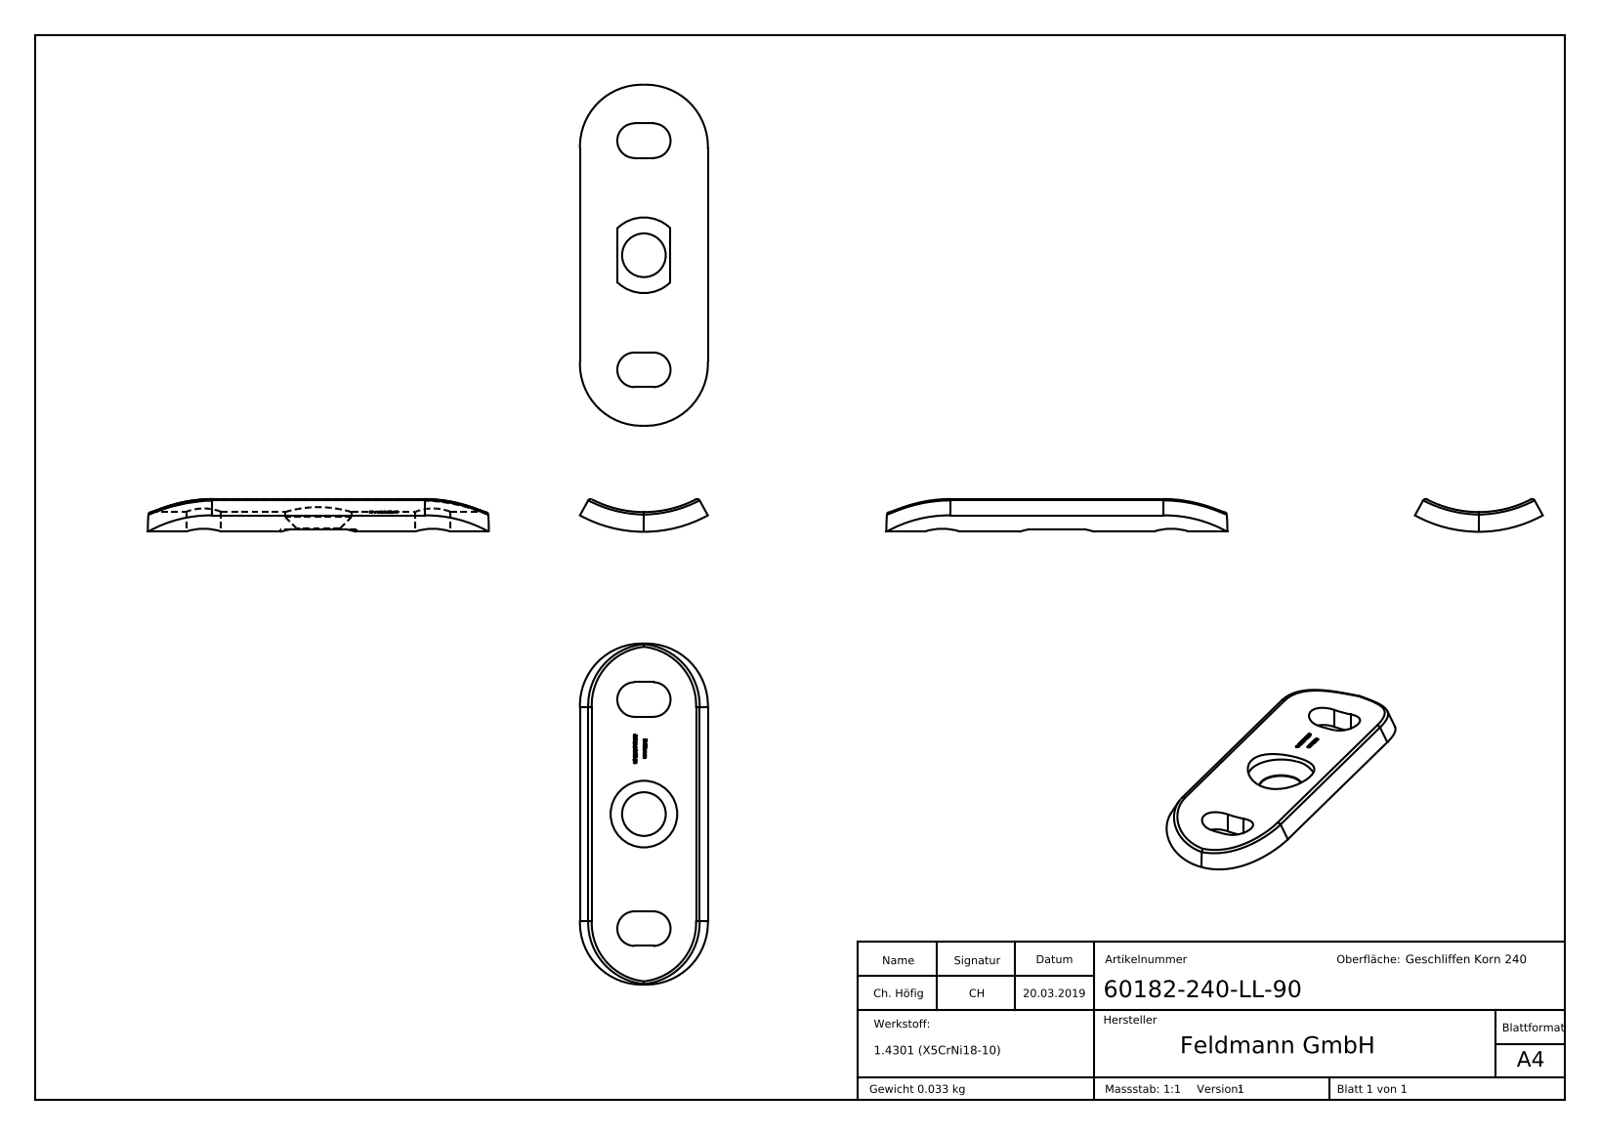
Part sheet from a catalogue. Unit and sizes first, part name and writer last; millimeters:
Units: millimetres
Overall size (bounding box): 64 × 24 × 6.15
Round holes (diameter × count): ⌀8.2 ×1, ⌀12.5 ×1
Partial cylindrical surfaces — rounded edges, fillets, slot ends (radius × count): R3.25 ×4, R12 ×4, R0.5 ×2, R7.1 ×1, R21.2 ×1, R21.3 ×1, R24.9 ×1
Main face-to-face distances: 6.5, 43, 49.5, 36.5, 1.85, 2.32, 1.93, 1.98, 1.96, 1.9
Volume: 4 228 mm³ · Surface area: 3 228 mm²
Bodies: 1 solid, 303 faces (122 planar, 53 cylindrical, 128 other)
Part name (STEP PRODUCT): 60182-240-LL-90
STEP written by: SolidWorks 2015 (CONFIG_CONTROL_DESIGN)
